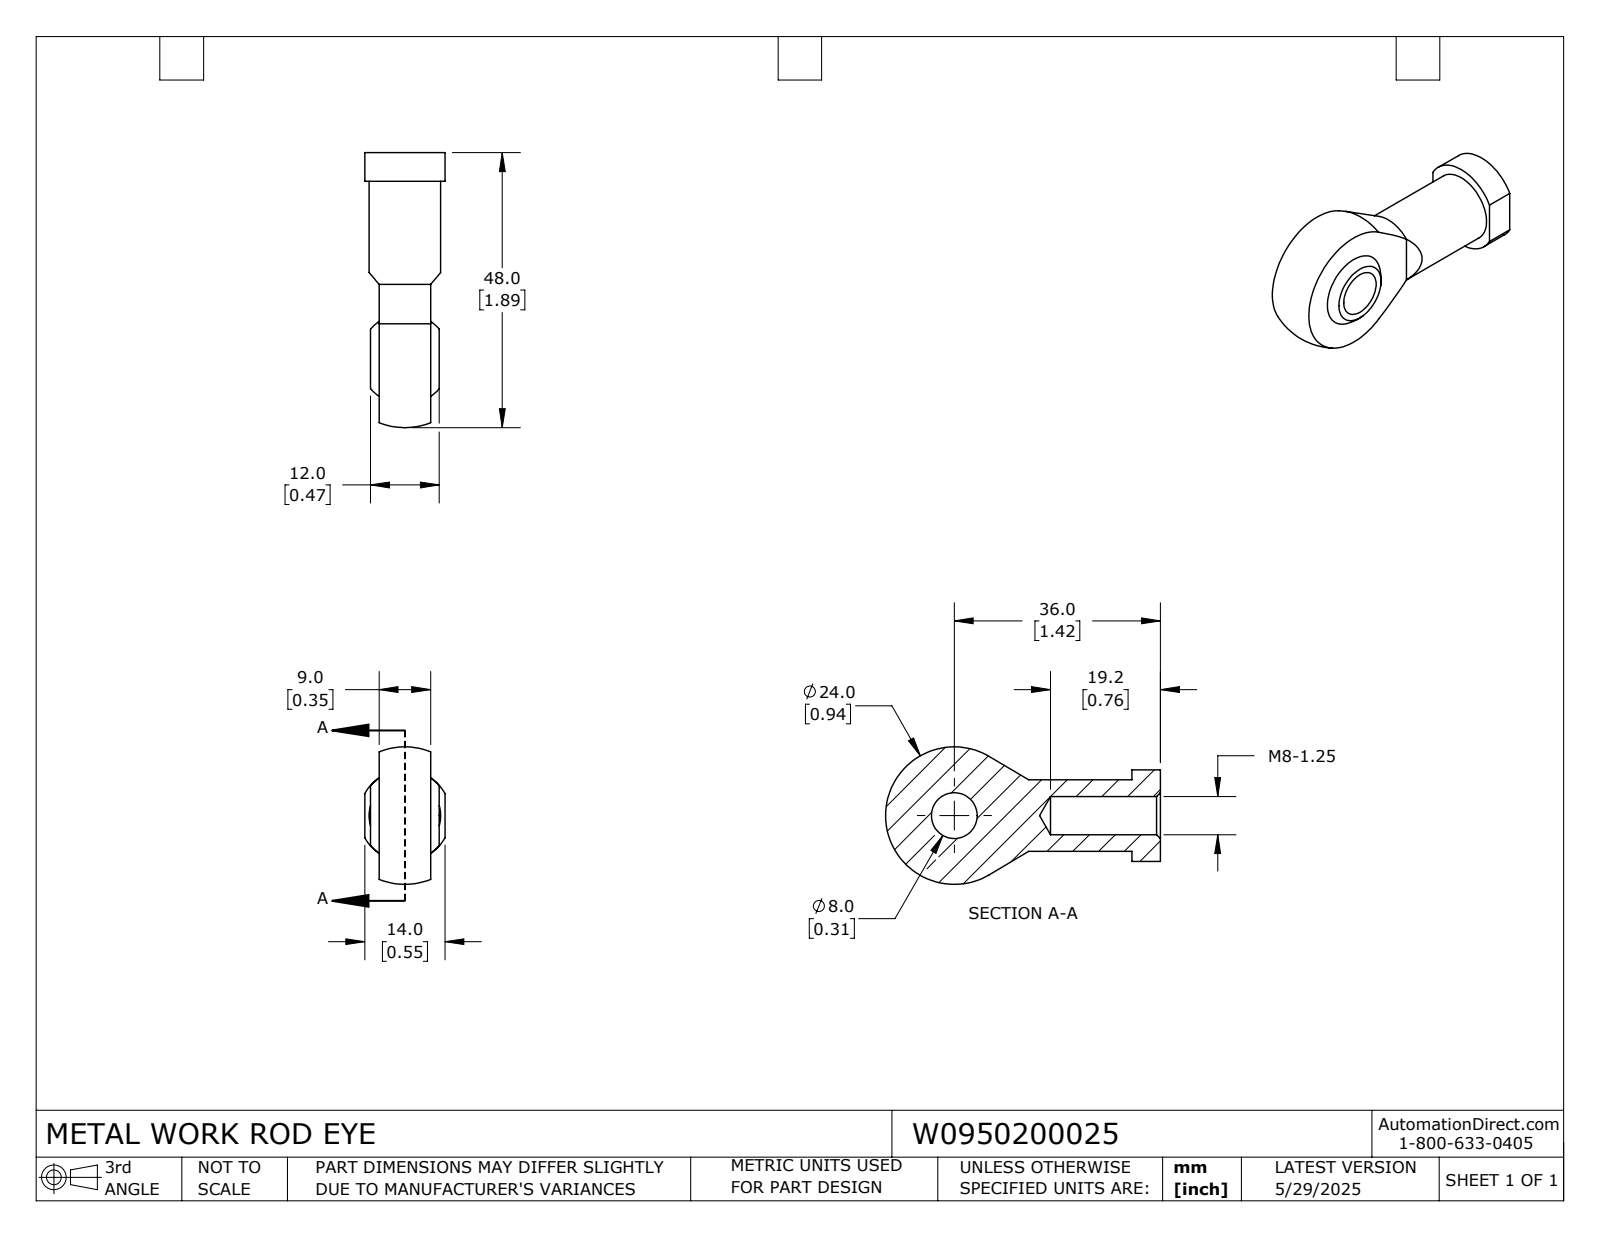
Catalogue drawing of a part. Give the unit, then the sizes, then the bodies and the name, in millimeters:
Units: millimetres
Overall size (bounding box): 48 × 24 × 14
Round holes (diameter × count): ⌀6.65 ×1, ⌀8 ×1
Round bosses / shafts (diameter × count): ⌀12.5 ×1
Partial cylindrical surfaces — rounded edges, fillets, slot ends (radius × count): R8 ×1
Main face-to-face distances: 9, 2.5, 11.5, 1, 13, 1.5, 10.5, 5, 14, 12
Volume: 6 321 mm³ · Surface area: 3 318 mm²
Bodies: 1 solid, 28 faces (10 planar, 8 cylindrical, 10 other)
Part name (STEP PRODUCT): W0950200025
STEP written by: SolidWorks 2024 (CONFIG_CONTROL_DESIGN)
